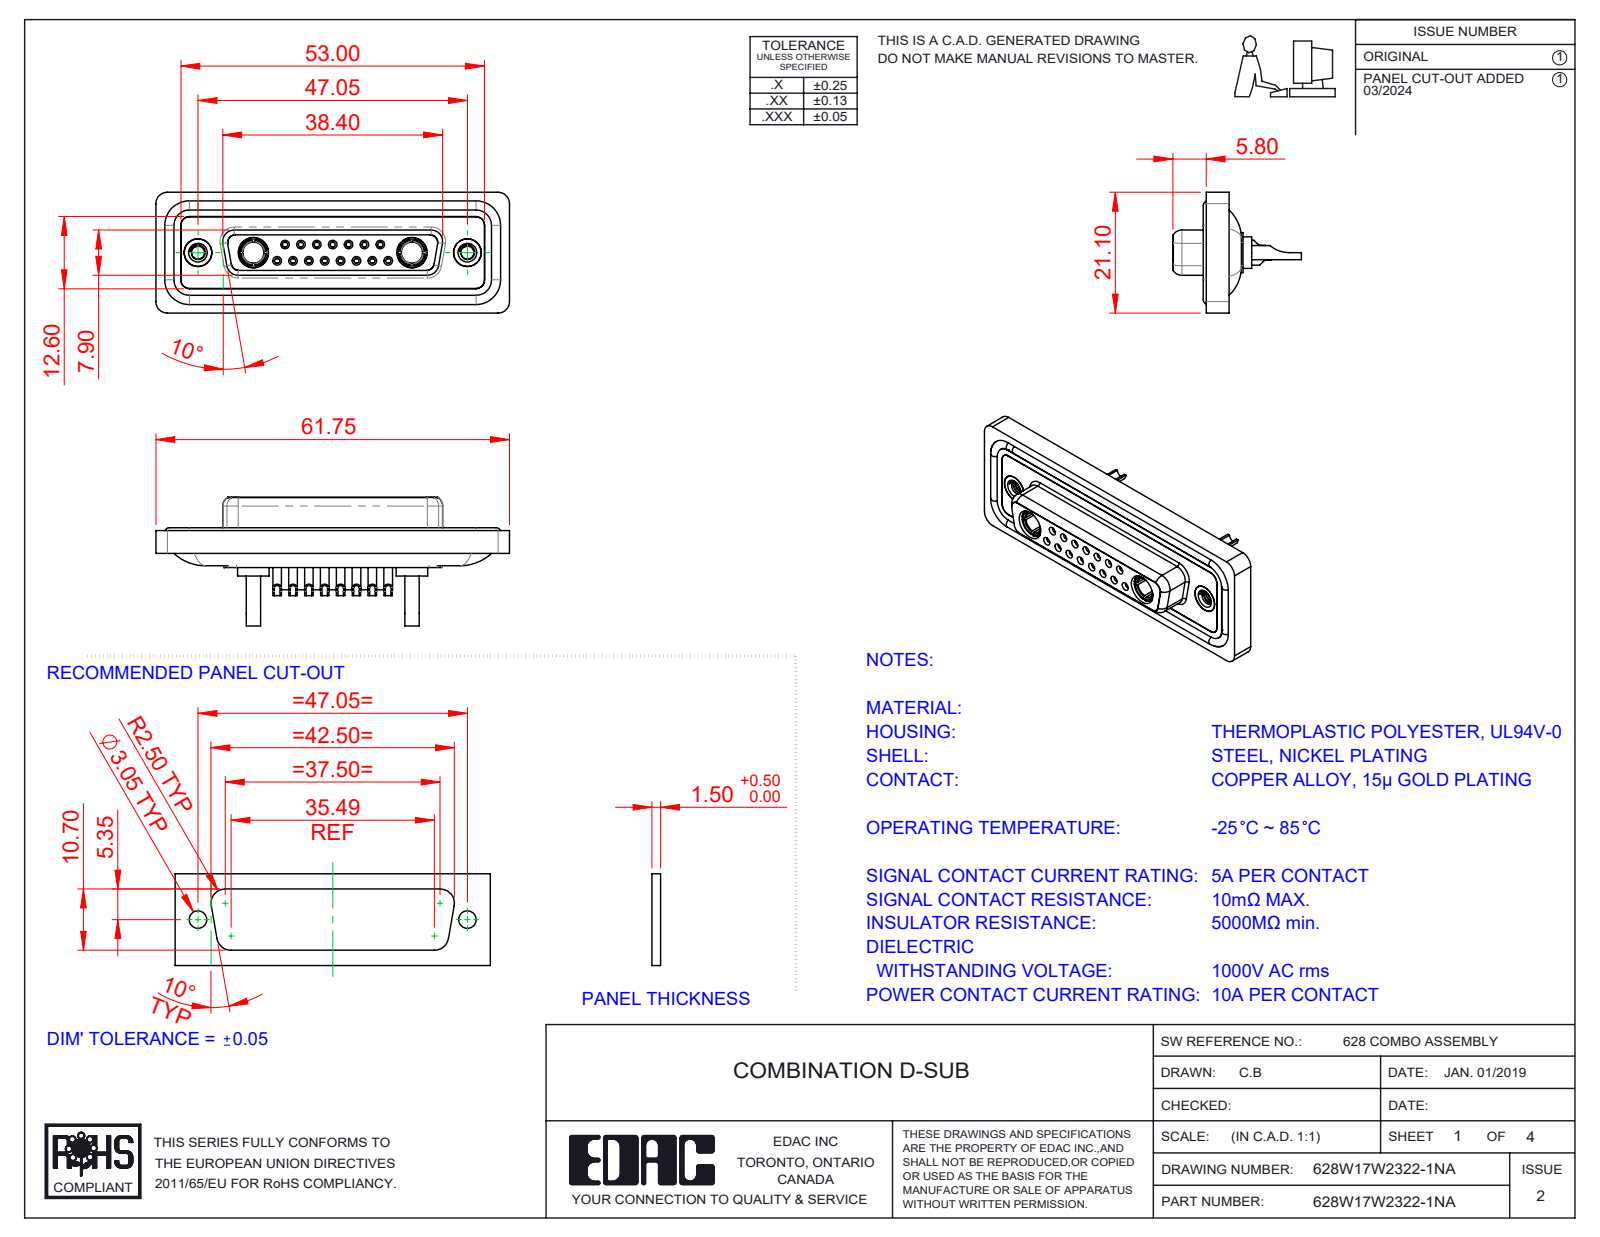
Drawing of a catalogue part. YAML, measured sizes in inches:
part_name: "628Combo Waterproof Housing_25 Contacts; 628Combo Threaded Rivet_A; 628Combo Shell Front_25 Contacts; 628Combo Contact Row 1_22 (+5 more)"
step_written_by: "SolidWorks 2023 (CONFIG_CONTROL_DESIGN)"
units: inches
bodies: {solids: 26, faces: 1367, planar: 422, cylindrical: 557, other: 388}
overall_size: [2.431, 0.884, 0.831]
volume: 0.51
surface_area: 21.87
round_holes:
  - {diameter: 0.035, count: 15}
  - {diameter: 0.039, count: 15}
  - {diameter: 0.043, count: 15}
  - {diameter: 0.059, count: 15}
  - {diameter: 0.079, count: 15}
  - {diameter: 0.063, count: 8}
  - {diameter: 0.067, count: 7}
  - {diameter: 0.191, count: 4}
  - {diameter: 0.067, count: 2}
  - {diameter: 0.089, count: 2}
  - {diameter: 0.146, count: 2}
  - {diameter: 0.157, count: 2}
round_bosses_or_shafts:
  - {diameter: 0.087, count: 15}
  - {diameter: 0.063, count: 11}
  - {diameter: 0.217, count: 2}
  - {diameter: 0.205, count: 2}
  - {diameter: 0.195, count: 2}
  - {diameter: 0.195, count: 2}
  - {diameter: 0.189, count: 2}
  - {diameter: 0.187, count: 2}
partial_cylinders:
  - {radius: 0.059, count: 22}
  - {radius: 0.079, count: 18}
  - {radius: 0.053, count: 8}
  - {radius: 0.063, count: 8}
  - {radius: 0.039, count: 6}
  - {radius: 0.01, count: 4}
  - {radius: 0.02, count: 4}
  - {radius: 0.024, count: 4}
face_to_face_distances: [0.016, 0.071, 0.293, 0.222, 0.26, 0.02, 0.278, 0.063, 0.114, 0.043]
hole_center_spacings: [0.124, 0.109, 0.327, 0.218, 0.198, 0.198, 0.295, 0.436]
